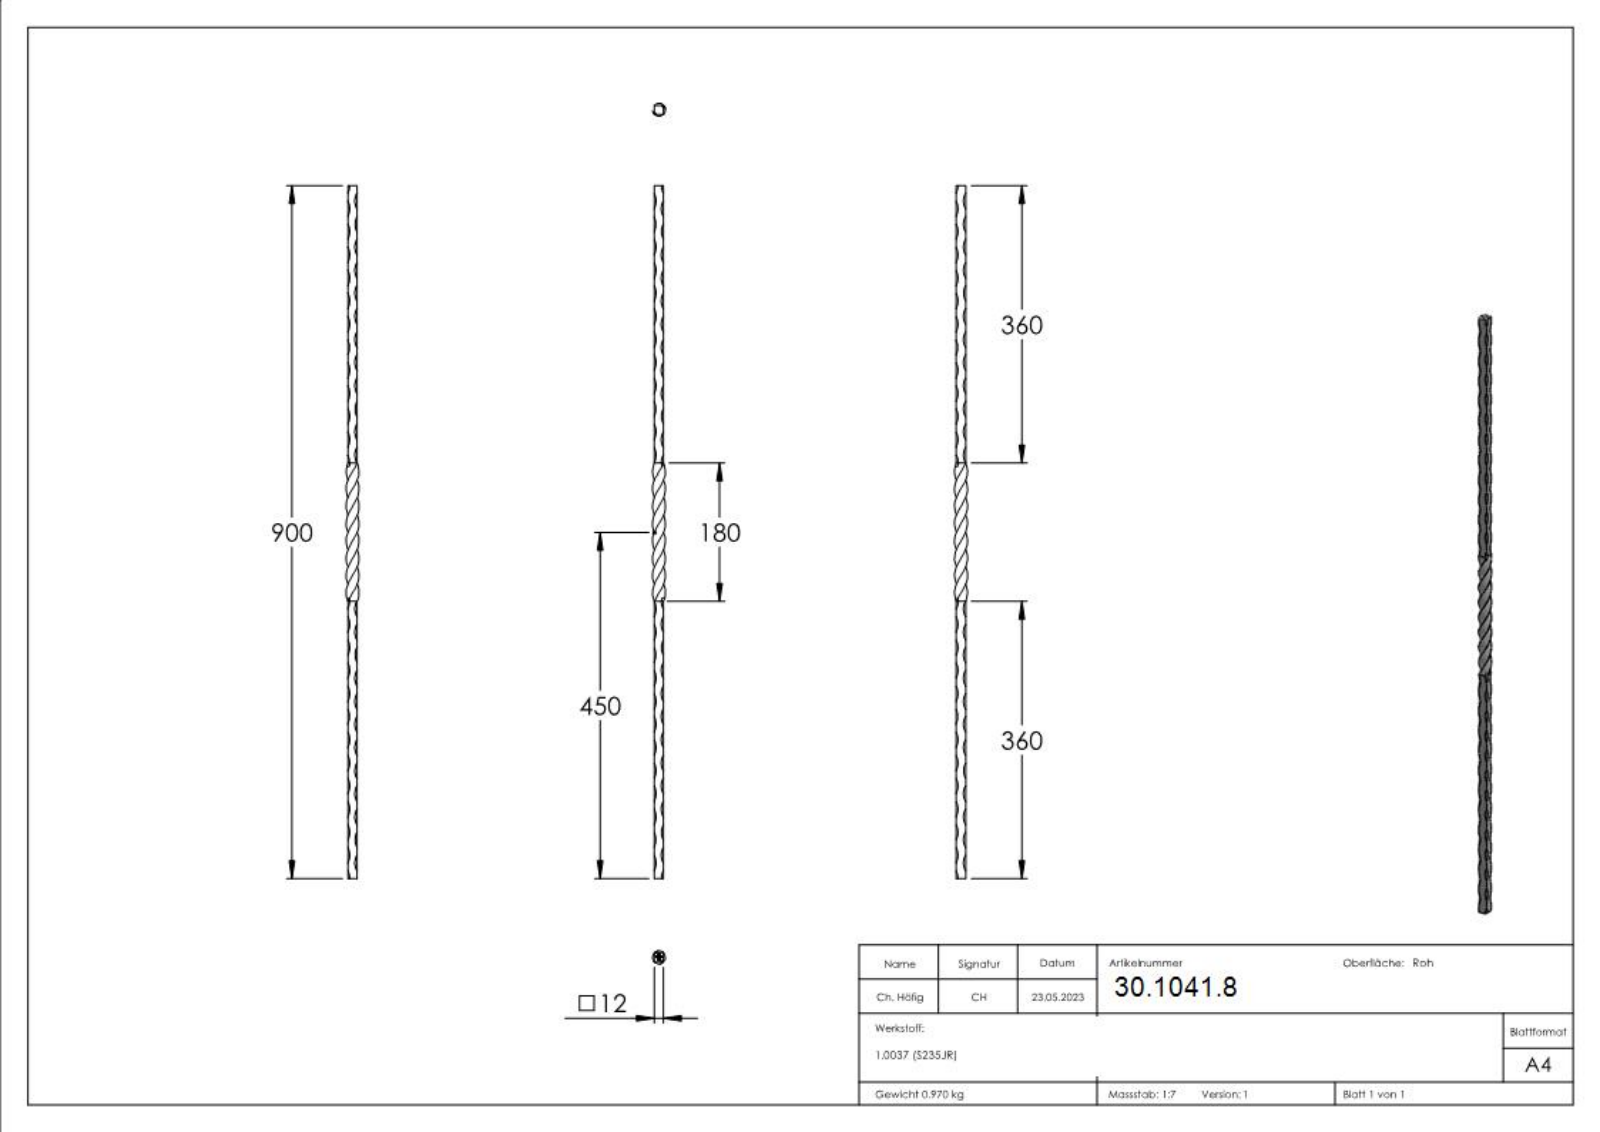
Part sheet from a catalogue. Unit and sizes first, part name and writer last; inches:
Units: inches
Overall size (bounding box): 35.433 × 0.67 × 0.67
Main face-to-face distances: 0.472, 35.433, 35.429, 0.022, 0.04, 0.045, 0.049, 0.063, 0.018, 0.035
Volume: 7.59 in³ · Surface area: 65.78 in²
Bodies: 1 solid, 313 faces (123 planar, 0 cylindrical, 190 other)
Part name (STEP PRODUCT): 1113
STEP written by: SolidWorks 2018 (CONFIG_CONTROL_DESIGN)
